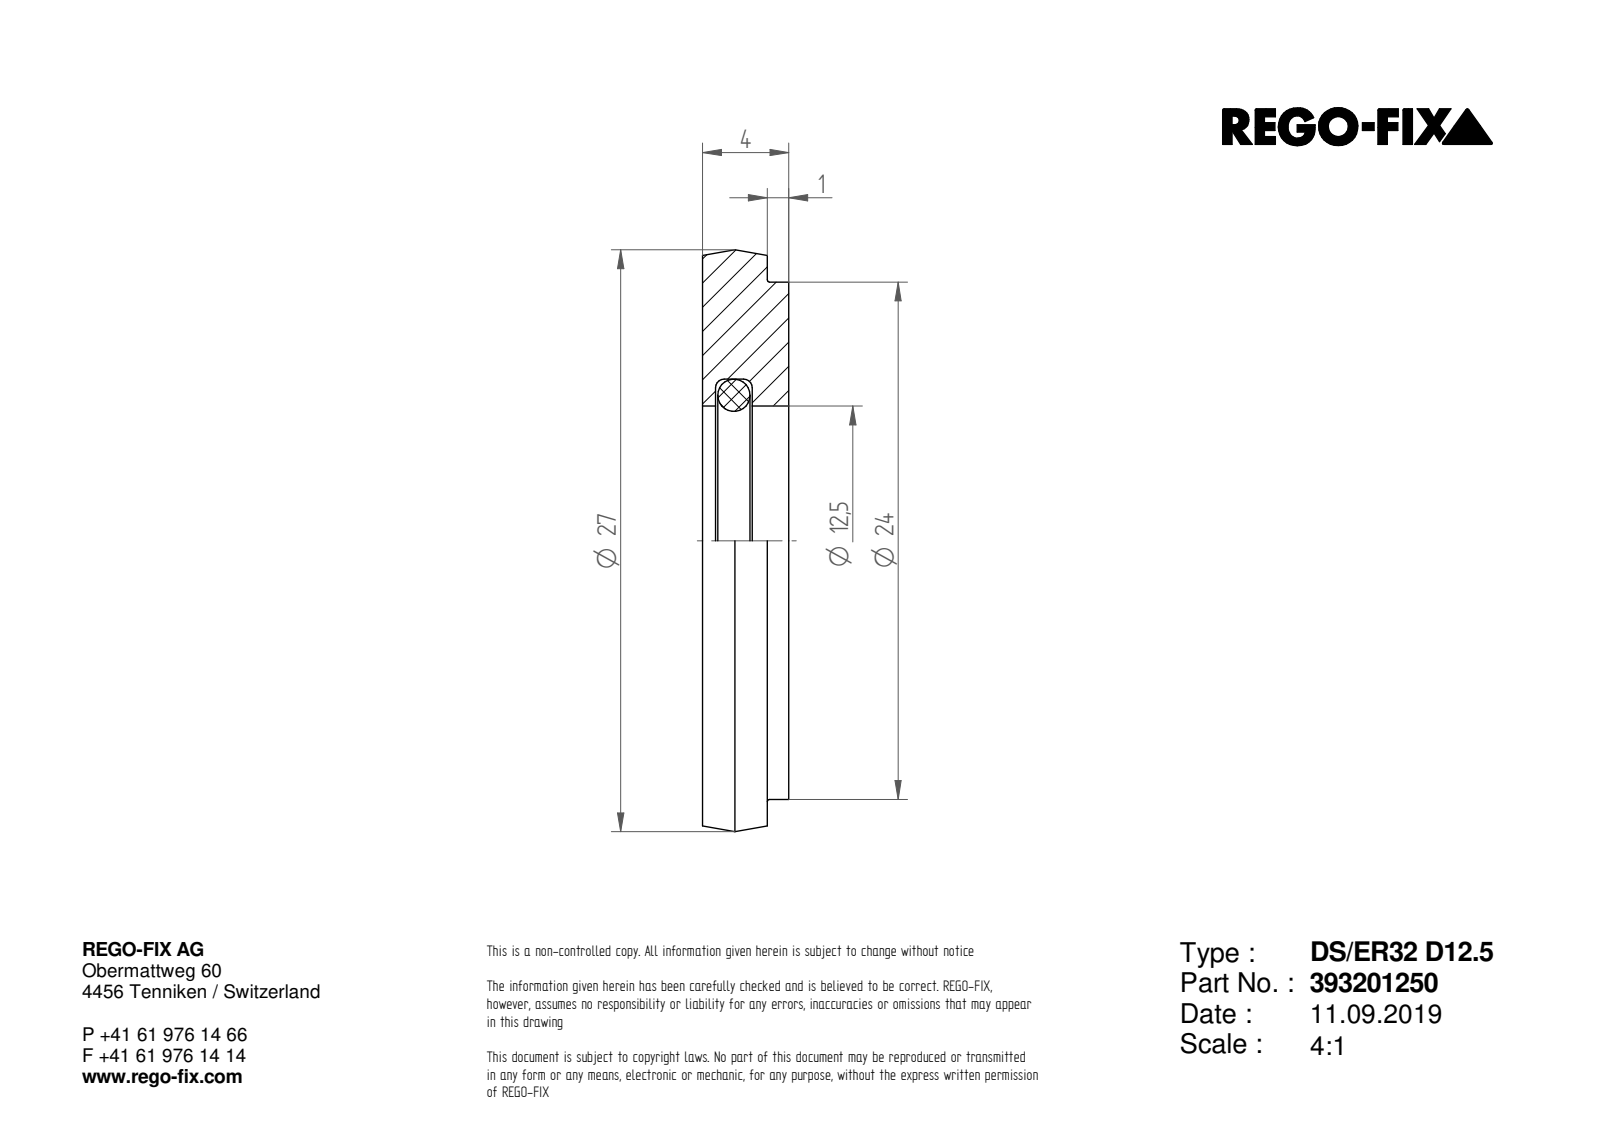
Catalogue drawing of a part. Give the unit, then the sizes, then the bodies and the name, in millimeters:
Units: millimetres
Overall size (bounding box): 27 × 27 × 4
Round holes (diameter × count): ⌀12.5 ×1
Round bosses / shafts (diameter × count): ⌀27 ×1, ⌀24 ×1
Main face-to-face distances: 4, 1, 3
Volume: 1 679 mm³ · Surface area: 1 383 mm²
Bodies: 1 solid, 7 faces (3 planar, 3 cylindrical, 1 other)
Part name (STEP PRODUCT): NOCUT
STEP written by: SIEMENS PLM Software Solid Edge ST10 (AUTOMOTIVE_DESIGN)
